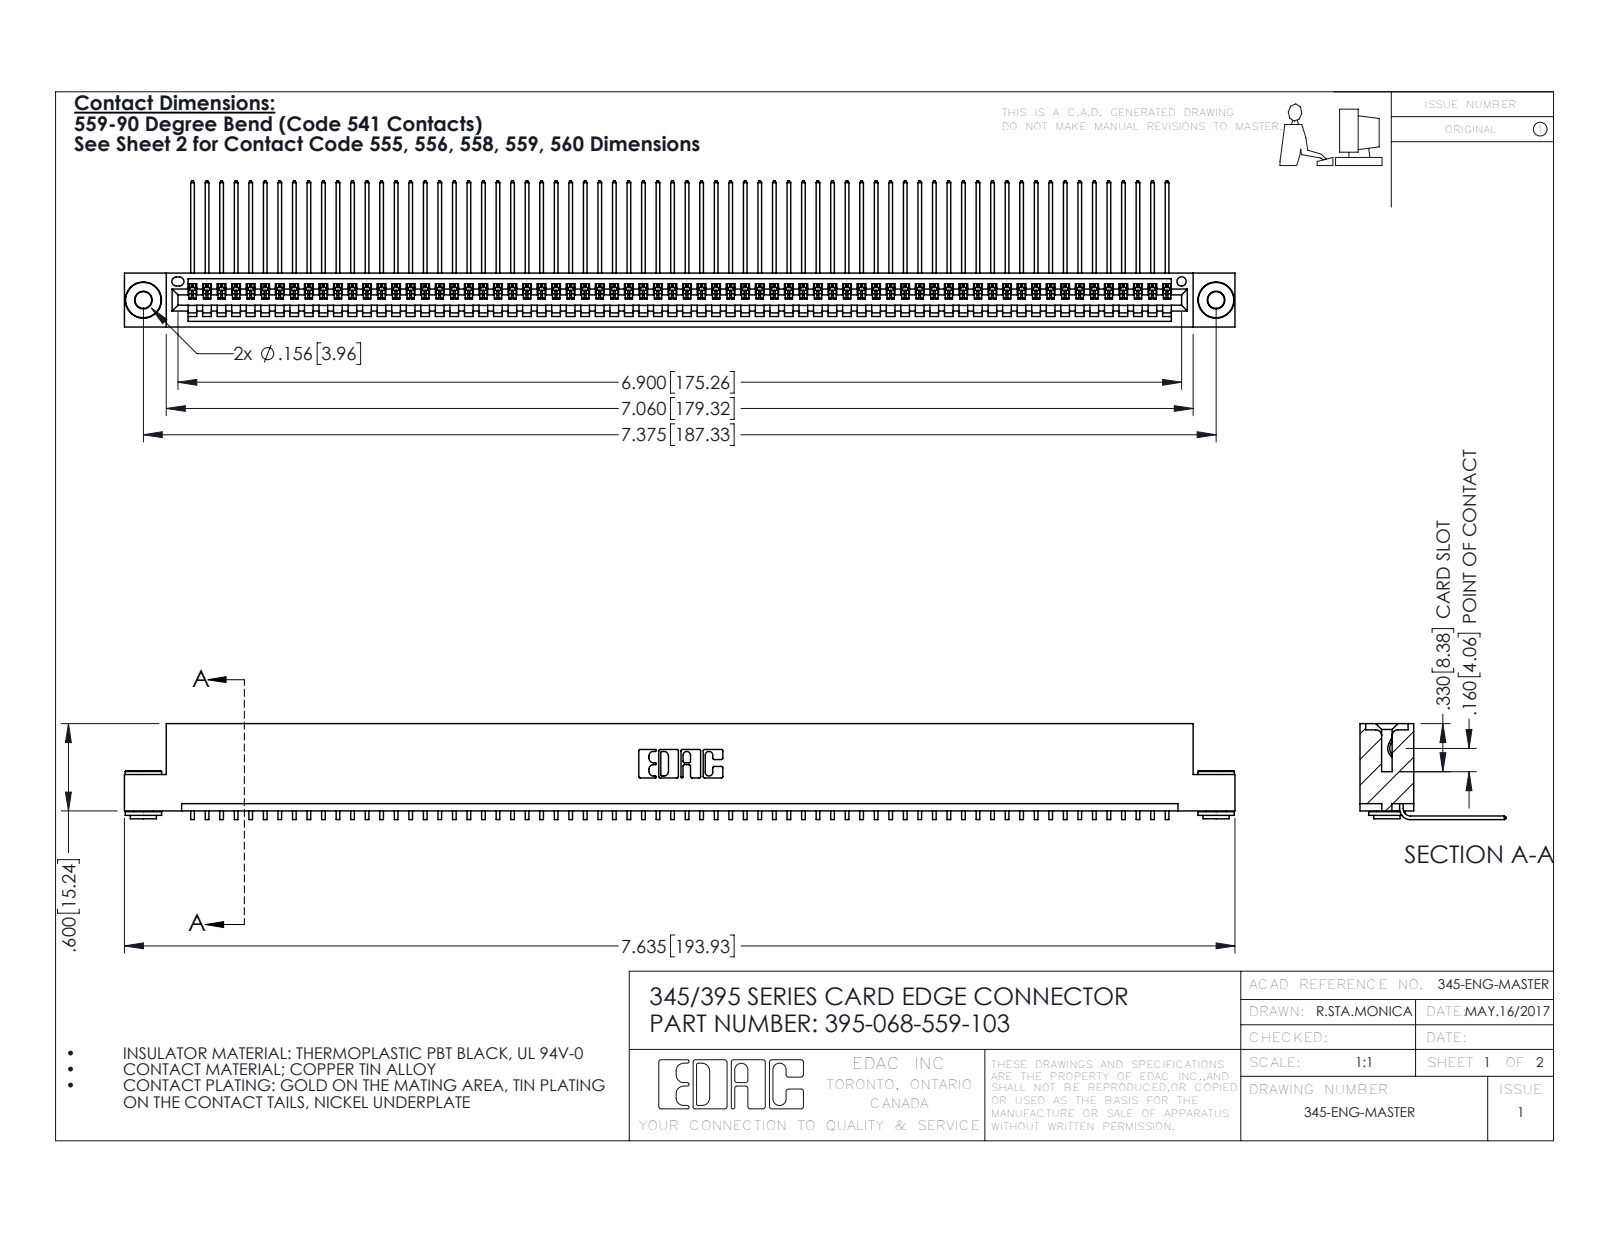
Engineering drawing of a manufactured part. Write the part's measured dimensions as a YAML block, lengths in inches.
part_name: "345-250-002_345-250-002-102; 395-068-559-103; 345 Part_Flush Mounting Lugs - 0.156 Dia-TH; 345-292-001_558 559 Tail - 1"
step_written_by: "SolidWorks 2016 (CONFIG_CONTROL_DESIGN)"
units: inches
bodies: {solids: 71, faces: 4244, planar: 2946, cylindrical: 1290, other: 8}
overall_size: [7.635, 1.005, 0.659]
volume: 1.152
surface_area: 41.83
round_holes:
  - {diameter: 0.116, count: 2}
  - {diameter: 0.156, count: 2}
  - {diameter: 0.064, count: 1}
round_bosses_or_shafts:
  - {diameter: 0.25, count: 2}
  - {diameter: 0.18, count: 2}
  - {diameter: 0.136, count: 2}
partial_cylinders:
  - {radius: 0.006, count: 136}
  - {radius: 0.01, count: 22}
  - {radius: 0.007, count: 6}
  - {radius: 0.031, count: 6}
  - {radius: 0.026, count: 3}
  - {radius: 0.031, count: 2}
  - {radius: 0.04, count: 2}
  - {radius: 0.014, count: 1}
face_to_face_distances: [0.072, 0.298, 0.37, 0.2, 0.025, 0.098, 0.272, 0.225, 0.149, 0.072]
hole_center_spacings: [0.27, 7.139, 7.375]
